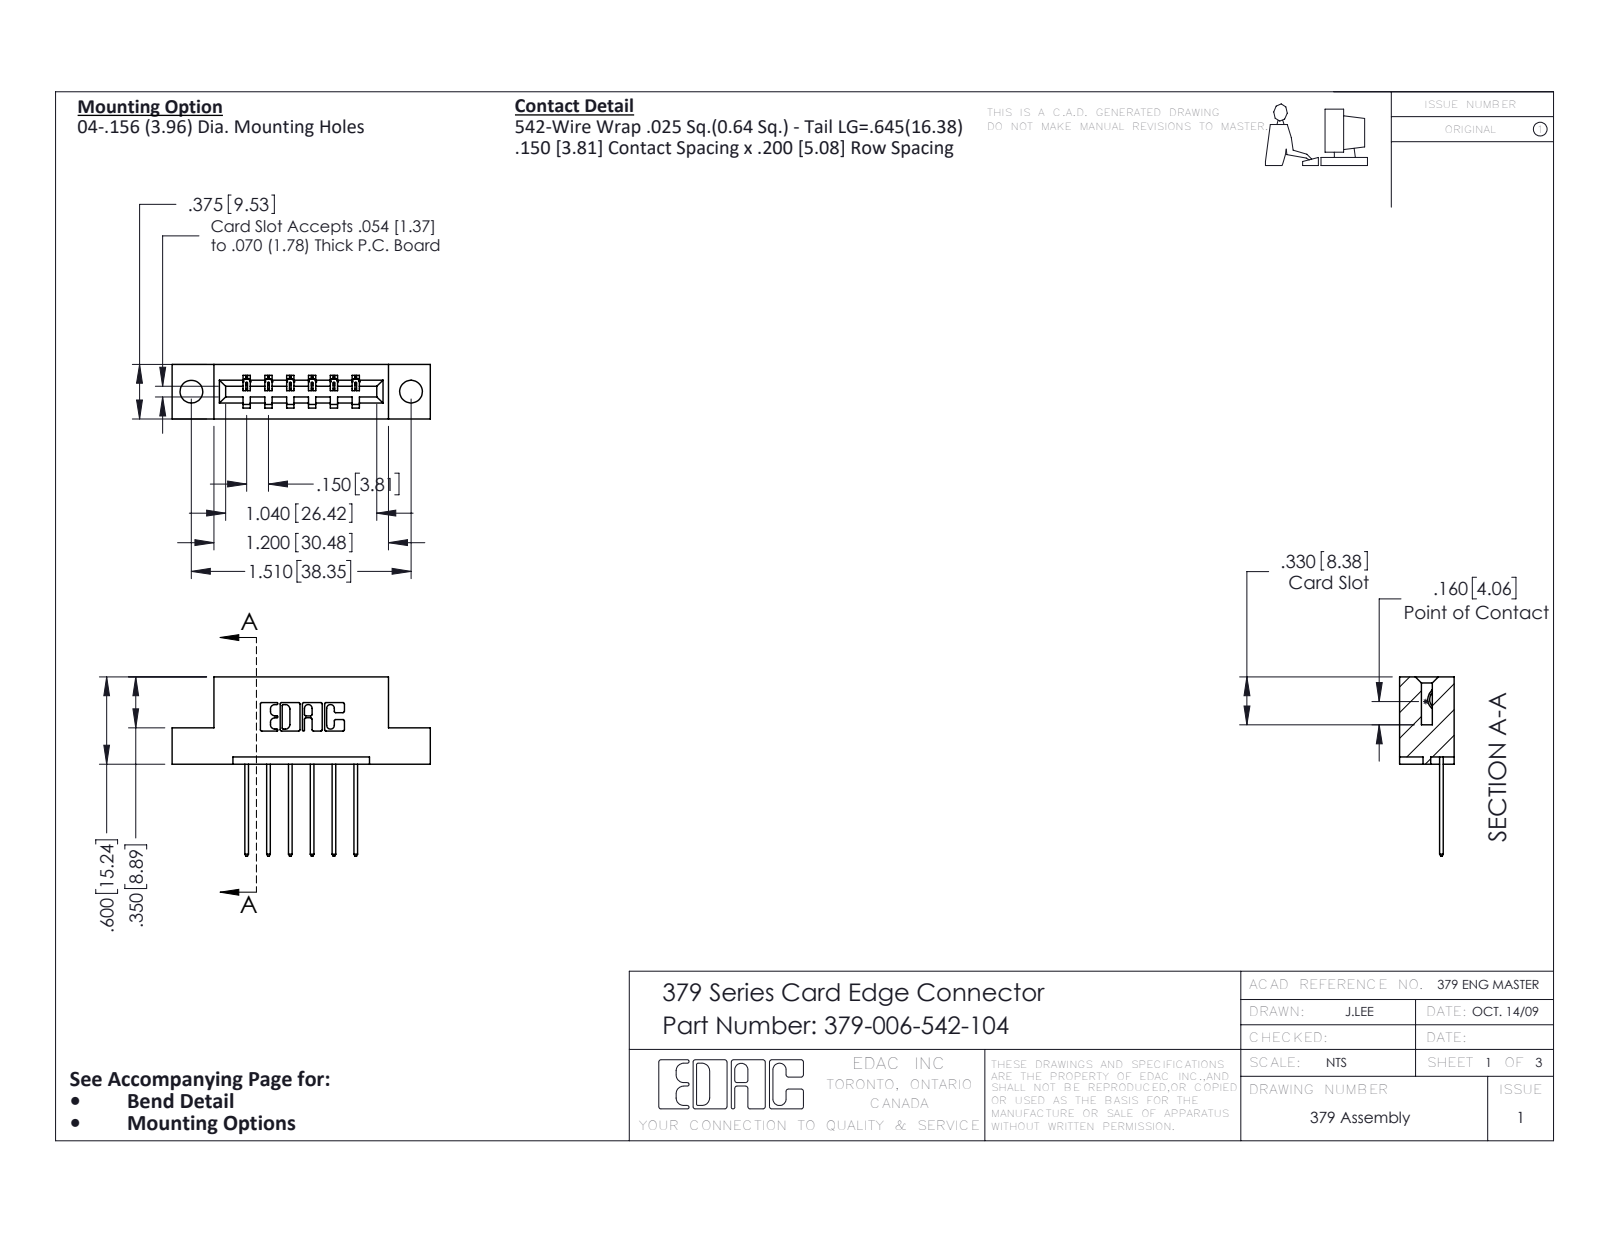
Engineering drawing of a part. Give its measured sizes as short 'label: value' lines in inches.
name: 379-006-542-104; 379 Part_Flush - .156 Dia - TH; 345-292-001_345-293-142
written by: SolidWorks 2016 (CONFIG_CONTROL_DESIGN)
unit: in
bodies: 7 solids, 462 faces (322 planar, 140 cylindrical, 0 other)
size: 1.775 × 1.232 × 0.375
volume: 0.258 in³; area: 6.254 in²
holes: 2× ⌀0.156
rounds: 22× R0.01, 12× R0.006, 12× R0.01, 6× R0.007, 6× R0.031, 3× R0.026, 1× R0.014, 1× R0.022
face distances: 0.3, 0.2, 0.375, 0.05, 0.15, 0.075, 0.1, 0.25, 0.35, 0.6
hole spacings: 1.51
